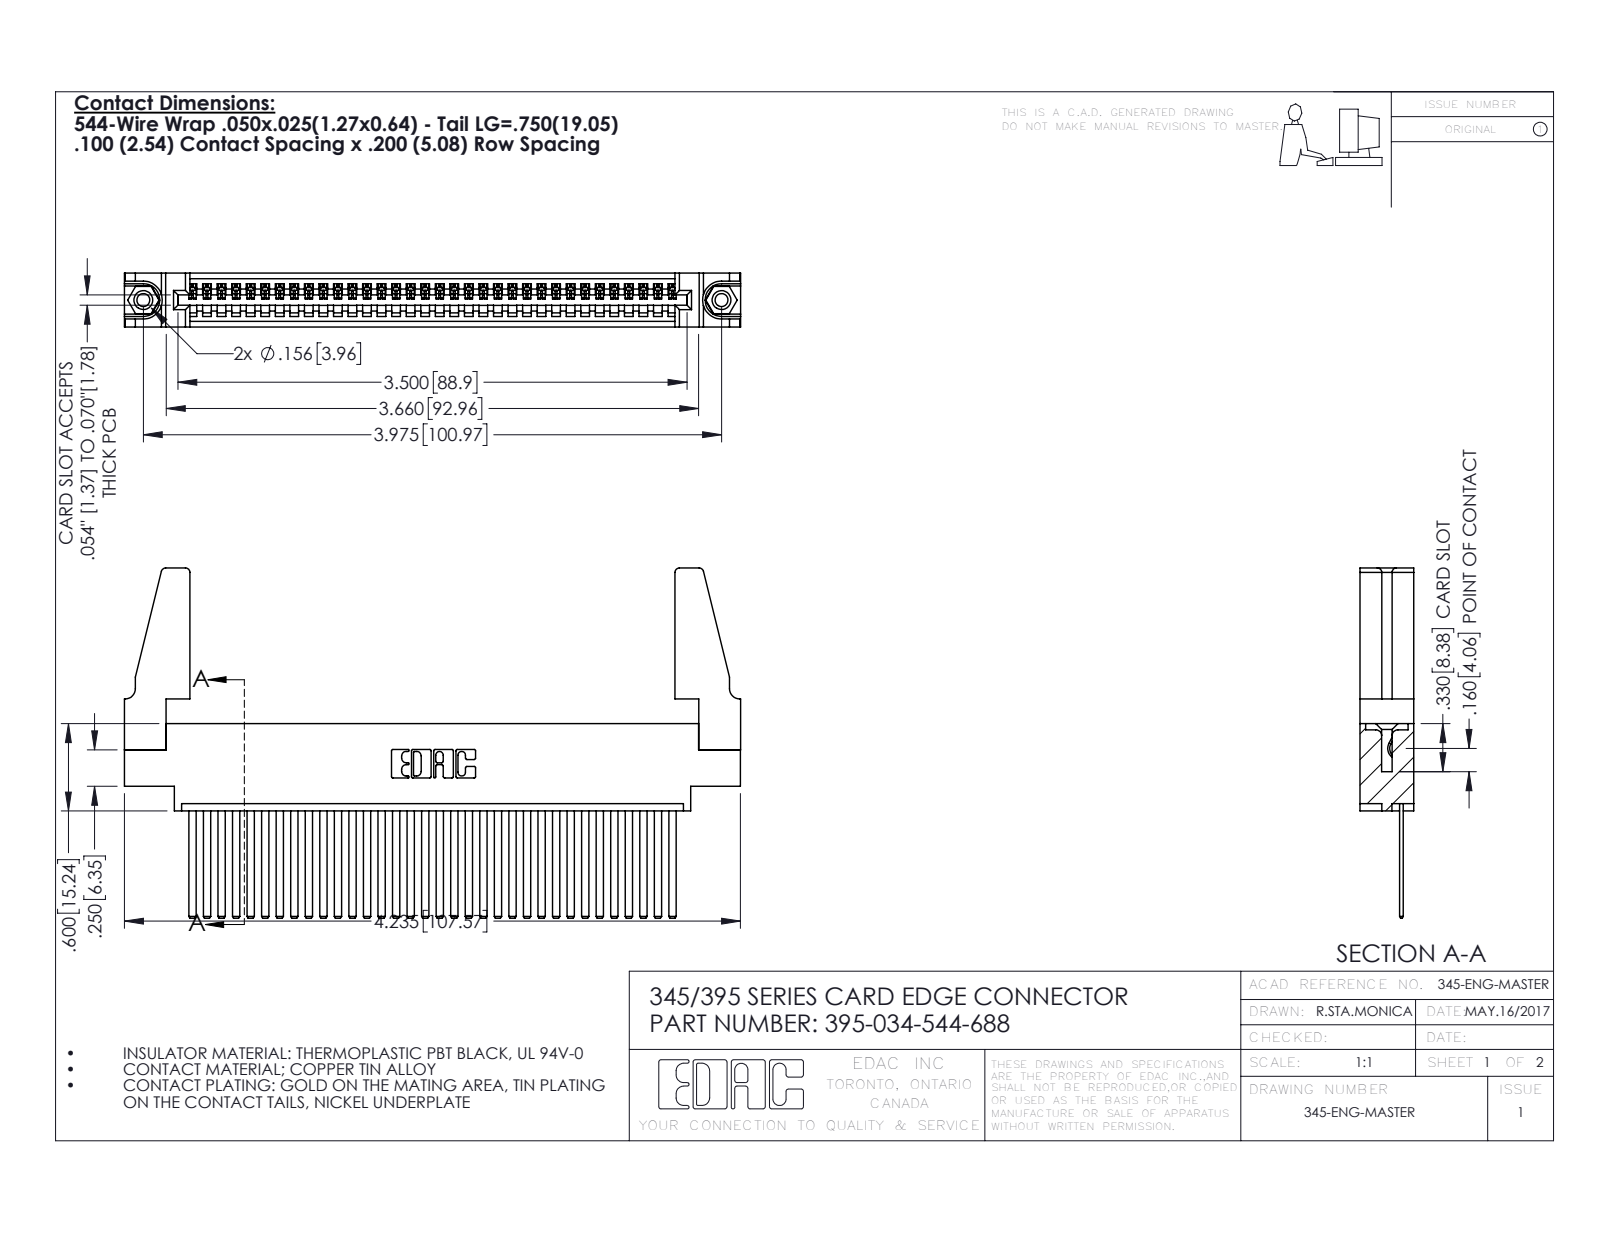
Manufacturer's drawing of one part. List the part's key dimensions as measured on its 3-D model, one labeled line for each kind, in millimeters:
Part name (STEP PRODUCT): 345-220-078_345-220-088; 395-034-544-688; 345-292-001_345-293-144; 345-250-001_345-250-001-102 (+1 more)
STEP written by: SolidWorks 2016 (CONFIG_CONTROL_DESIGN)
Units: millimetres
Bodies: 39 solids, 2022 faces (1380 planar, 626 cylindrical, 16 other)
Overall size (bounding box): 107.6 × 61.1 × 9.4
Volume: 13 700 mm³ · Surface area: 18 190 mm²
Round holes (diameter × count): ⌀2.3 ×2, ⌀3.2 ×2, ⌀4 ×2, ⌀1.6 ×1
Round bosses / shafts (diameter × count): ⌀3.9 ×2
Partial cylindrical surfaces — rounded edges, fillets, slot ends (radius × count): R0.2 ×68, R0.3 ×22, R0.8 ×8, R0.2 ×6, R0.8 ×6, R0.7 ×3, R0.8 ×2, R1 ×2
Main face-to-face distances: 1.8, 7.6, 9.4, 2.5, 6.9, 0.6, 5.1, 5.7, 4.4, 3.8
Hole centre spacings: 6.9, 95, 101
